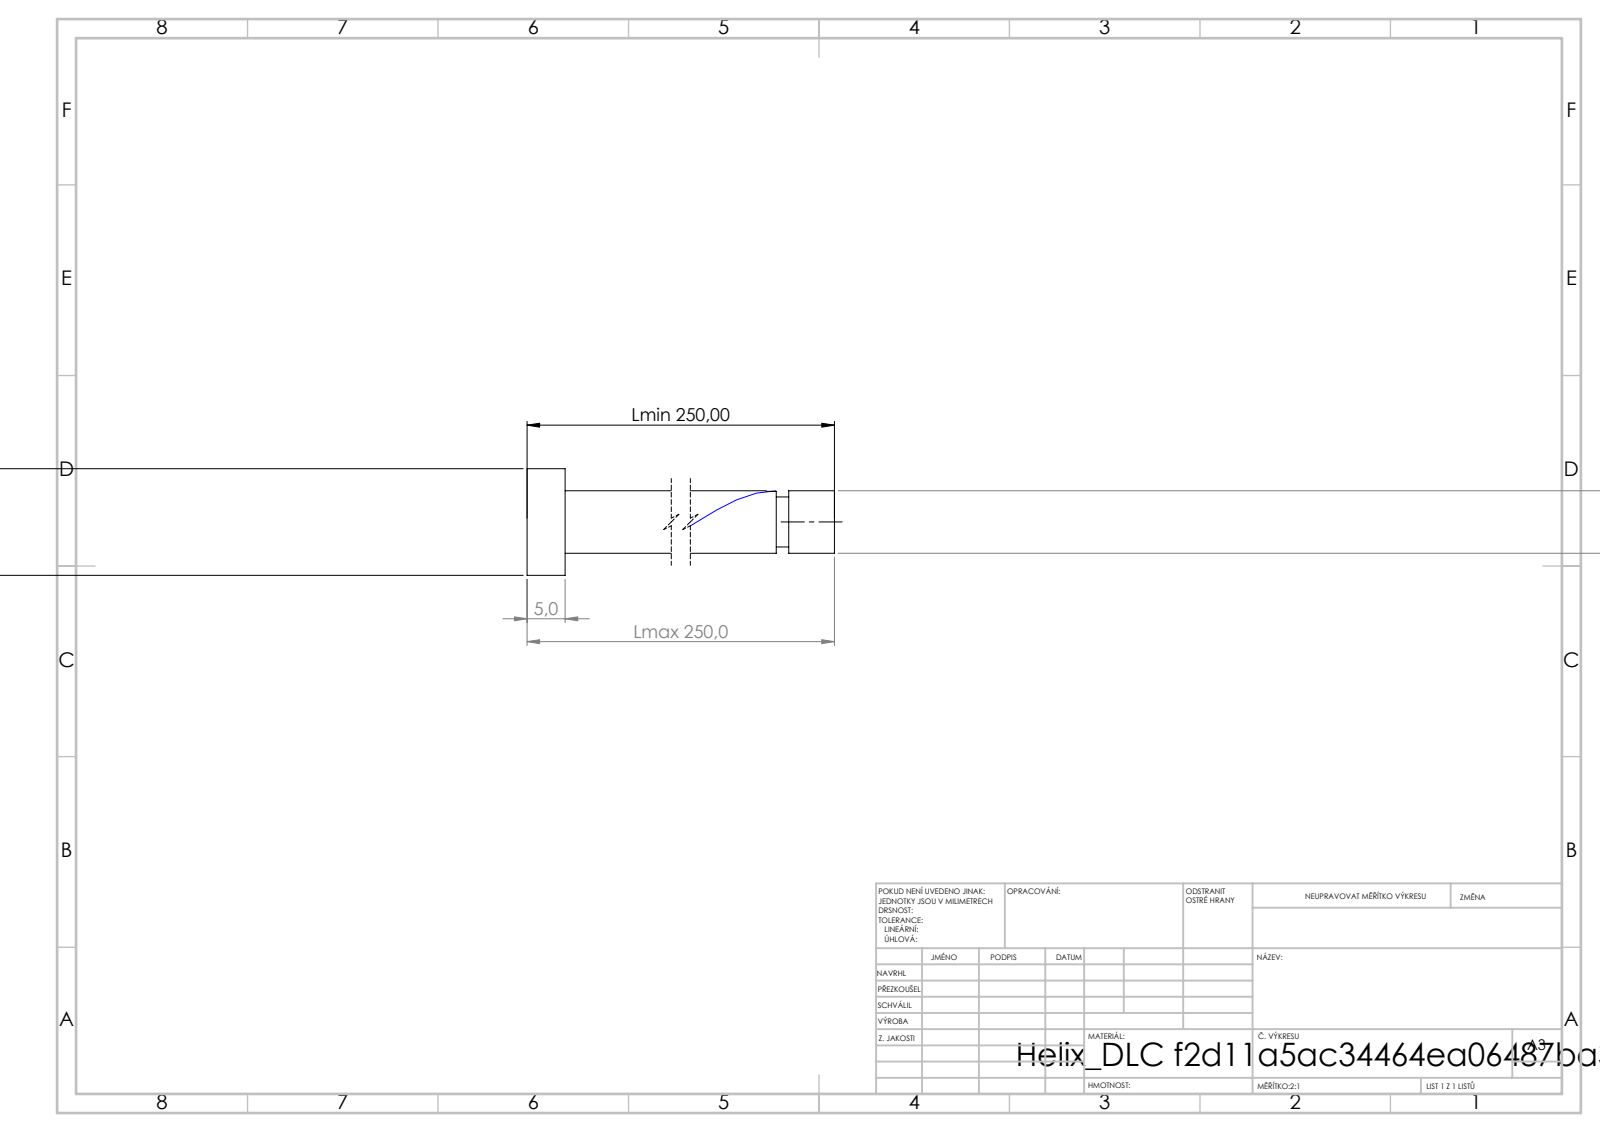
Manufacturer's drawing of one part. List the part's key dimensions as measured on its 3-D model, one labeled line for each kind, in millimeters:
STEP written by: SolidWorks 2019 (CONFIG_CONTROL_DESIGN)
Units: millimetres
Bodies: 1 solid, 21 faces (6 planar, 14 cylindrical, 1 other)
Overall size (bounding box): 250 × 14 × 14
Volume: 13 551 mm³ · Surface area: 6 990 mm²
Round bosses / shafts (diameter × count): ⌀14 ×1, ⌀8.2 ×1, ⌀6.56 ×1
Main face-to-face distances: 5, 250, 245, 244, 239, 6, 242.36, 237.36, 1.64, 7.64
